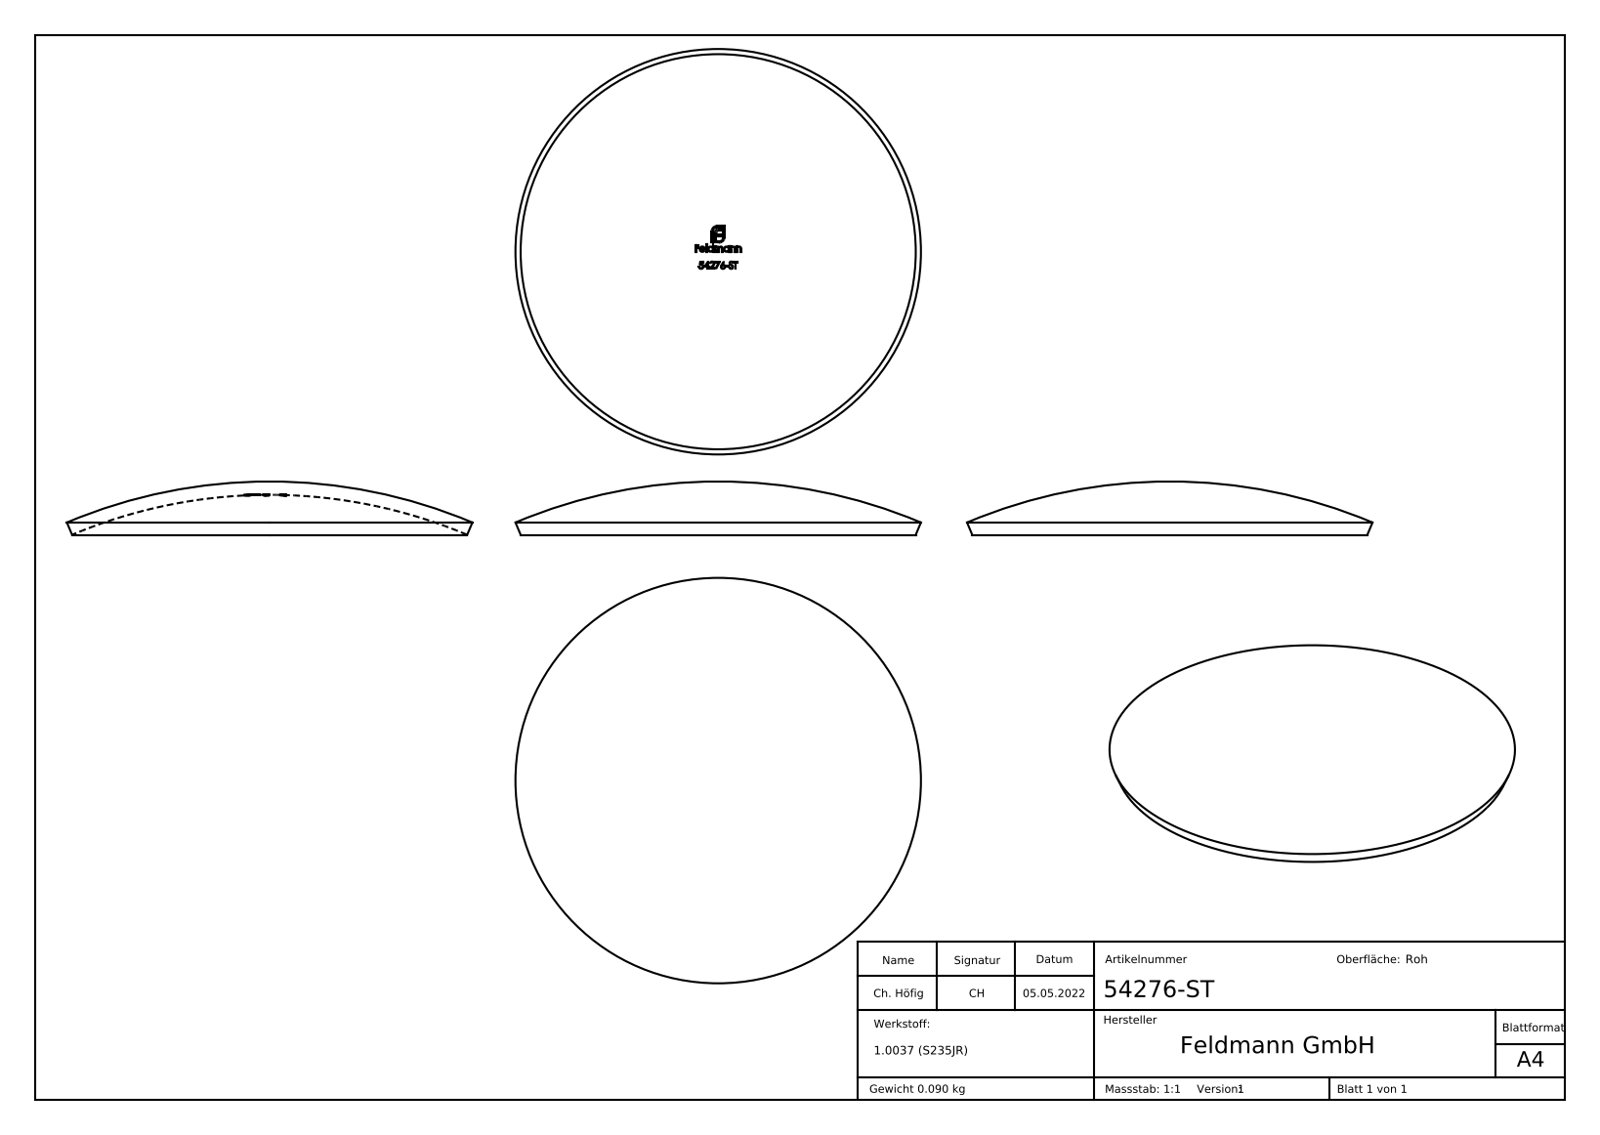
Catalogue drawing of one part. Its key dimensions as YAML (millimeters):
part_name: "54276-ST"
step_written_by: "SolidWorks 2018 (CONFIG_CONTROL_DESIGN)"
units: millimeters
bodies: {solids: 1, faces: 255, planar: 124, cylindrical: 0, other: 131}
overall_size: [76.1, 76.1, 10]
volume: 11536
surface_area: 9832
face_to_face_distances: [4.23, 1.26, 1.14, 0.99, 0.63, 0.58, 0.34, 2.02, 5.48, 3.96]
